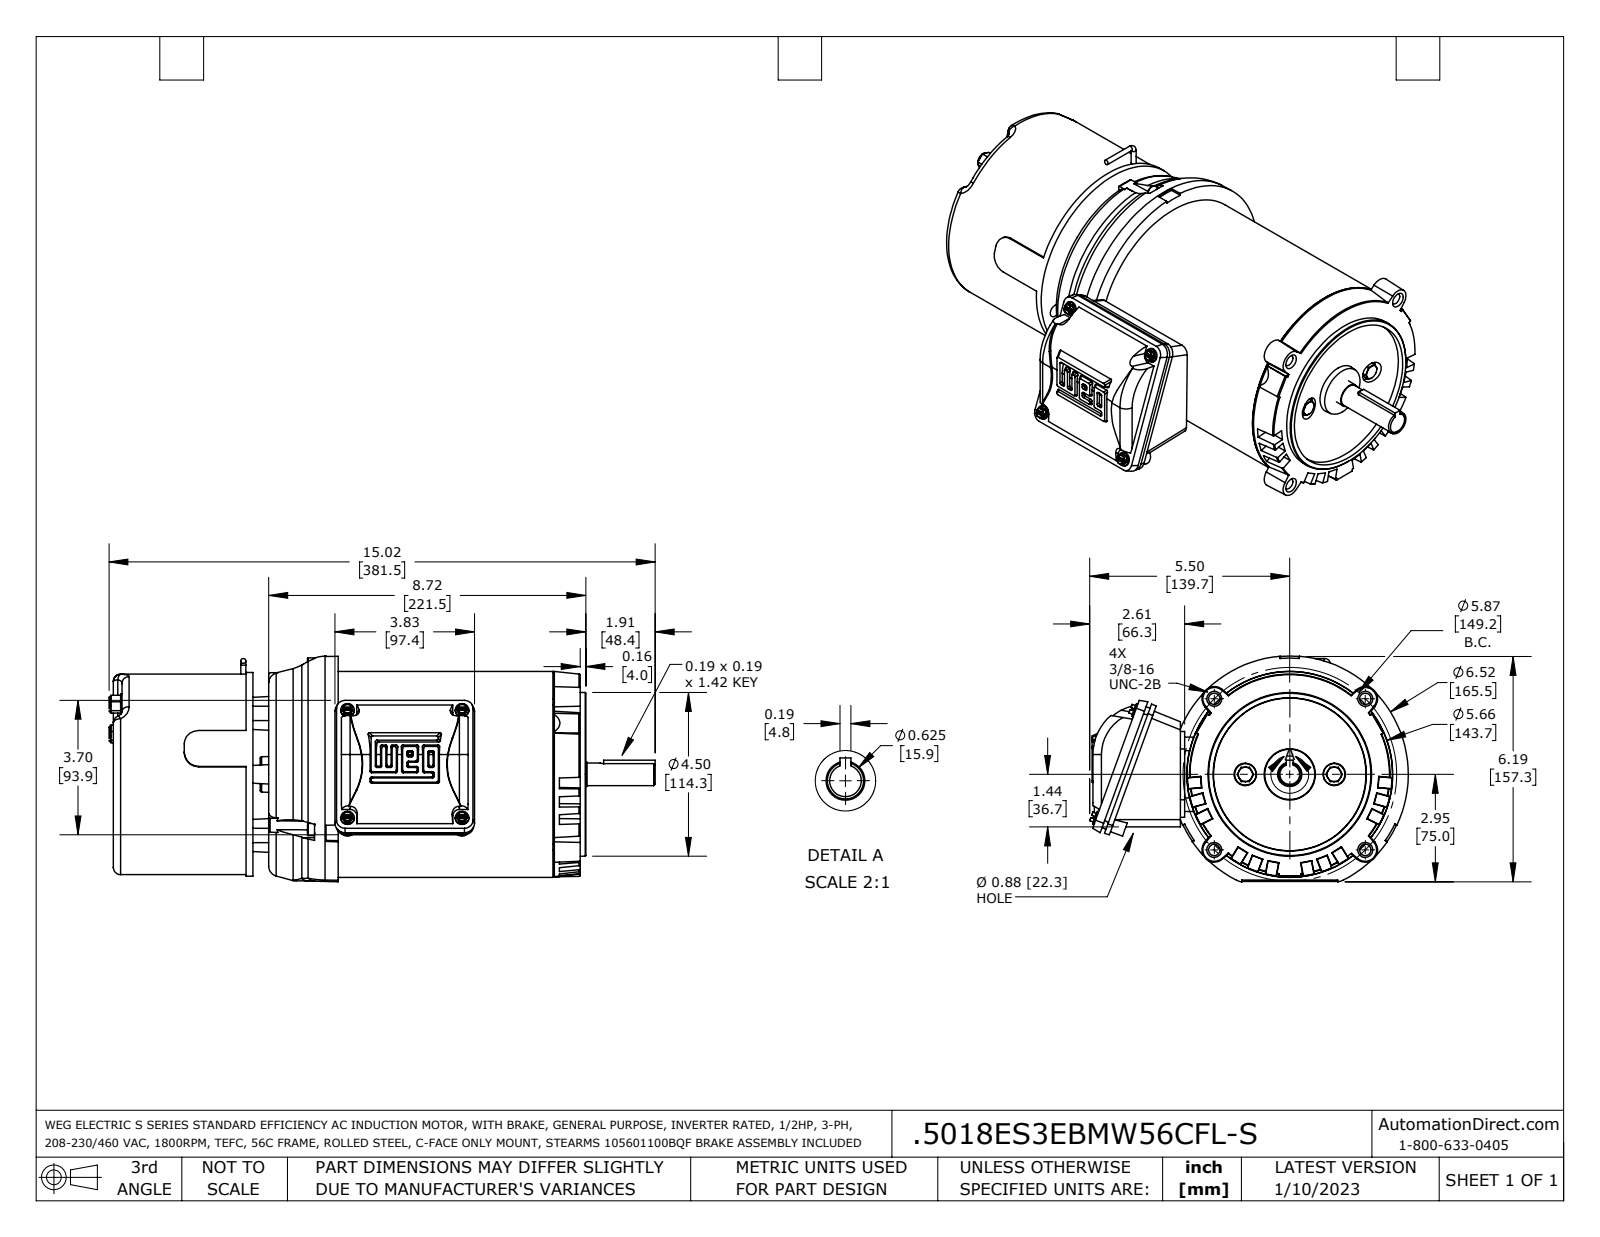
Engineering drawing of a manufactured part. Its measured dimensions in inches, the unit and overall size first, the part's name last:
Units: inches
Overall size (bounding box): 15.018 × 8.76 × 6.202
Round holes (diameter × count): ⌀0.236 ×4, ⌀0.313 ×4, ⌀0.25 ×2, ⌀0.28 ×2, ⌀0.37 ×2, ⌀0.5 ×1, ⌀3 ×1
Round bosses / shafts (diameter × count): ⌀0.374 ×4, ⌀0.187 ×4, ⌀0.335 ×3, ⌀0.197 ×3, ⌀0.551 ×2, ⌀0.437 ×2, ⌀0.138 ×2, ⌀5.659 ×1
Partial cylindrical surfaces — rounded edges, fillets, slot ends (radius × count): R0.047 ×38, R0.197 ×10, R0.205 ×8, R0.02 ×4, R0.276 ×4, R0.374 ×4, R0.48 ×4, R0.039 ×3
Main face-to-face distances: 5.906, 0.571, 6.476, 1.772, 7.52, 1.043, 1.614, 0.728, 2.343, 8.248
Hole centre spacings: 2.087, 2.937, 4.154, 4.463, 3.15, 0.718, 0.975, 1.483
Volume: 311.4 in³ · Surface area: 645.3 in²
Bodies: 15 solids, 1176 faces (471 planar, 231 cylindrical, 474 other)
Part name (STEP PRODUCT): W56C_3PH_TEFC_BM_15004_FL coord fxt
STEP written by: SolidWorks 2021 (AUTOMOTIVE_DESIGN)
